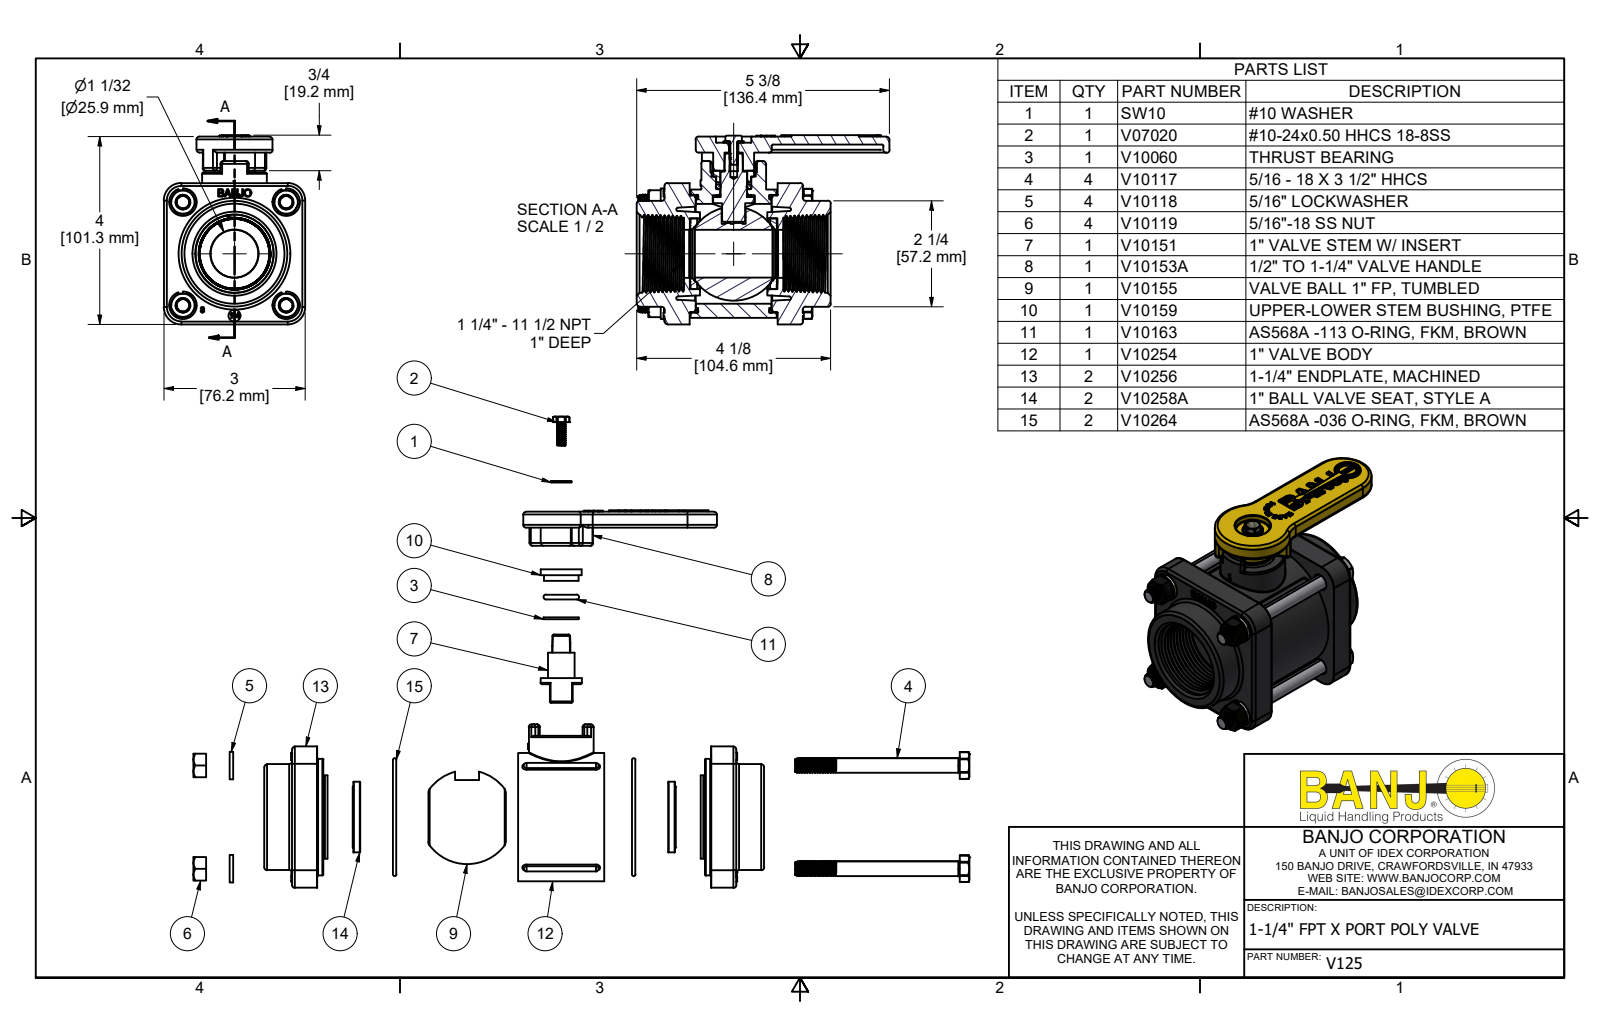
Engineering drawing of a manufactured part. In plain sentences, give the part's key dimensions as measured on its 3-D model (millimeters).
The part is named "V125; V10060; V10117; V10118 (+8 more)". Its 3-D file was written by "Autodesk Inventor 2022 (AUTOMOTIVE_DESIGN)". It is 27 solids with 2140 faces: 751 planar, 621 cylindrical and 768 other. Overall it measures 136.4 by 102 by 76.2 millimeters. Its volume is 338 200 cubic millimeters and its surface area 129 300 square millimeters. Round holes: 4 of diameter 6.4, 4 of diameter 8.2, 4 of diameter 9.3, 1 of diameter 2.3, 1 of diameter 3.7, 1 of diameter 5.1, 1 of diameter 5.2, 1 of diameter 6.4, 1 of diameter 9.6, 1 of diameter 13.5, 1 of diameter 14.3, 1 of diameter 14.5. Round bosses or shafts: 60 of diameter 6.8, 4 of diameter 14.8, 4 of diameter 8, 1 of diameter 69.2, 1 of diameter 62.9, 1 of diameter 58.5, 1 of diameter 57.2, 1 of diameter 45. Partial cylindrical surfaces (rounded edges, fillets, slot ends): 58 of radius 1.5, 32 of radius 0.8, 12 of radius 0.8, 8 of radius 3.4, 4 of radius 0.4, 4 of radius 2, 4 of radius 7.2, 4 of radius 9.4. The main face-to-face distances are 13.6, 61.1, 3.3, 76.2, 16.9, 57.8, 44.2, 74.7, 47.5, 15. The hole center spacings are 39.4, 55.7, 28.4, 67.2, 78.7, 9.2, 33.3, 65.3.
